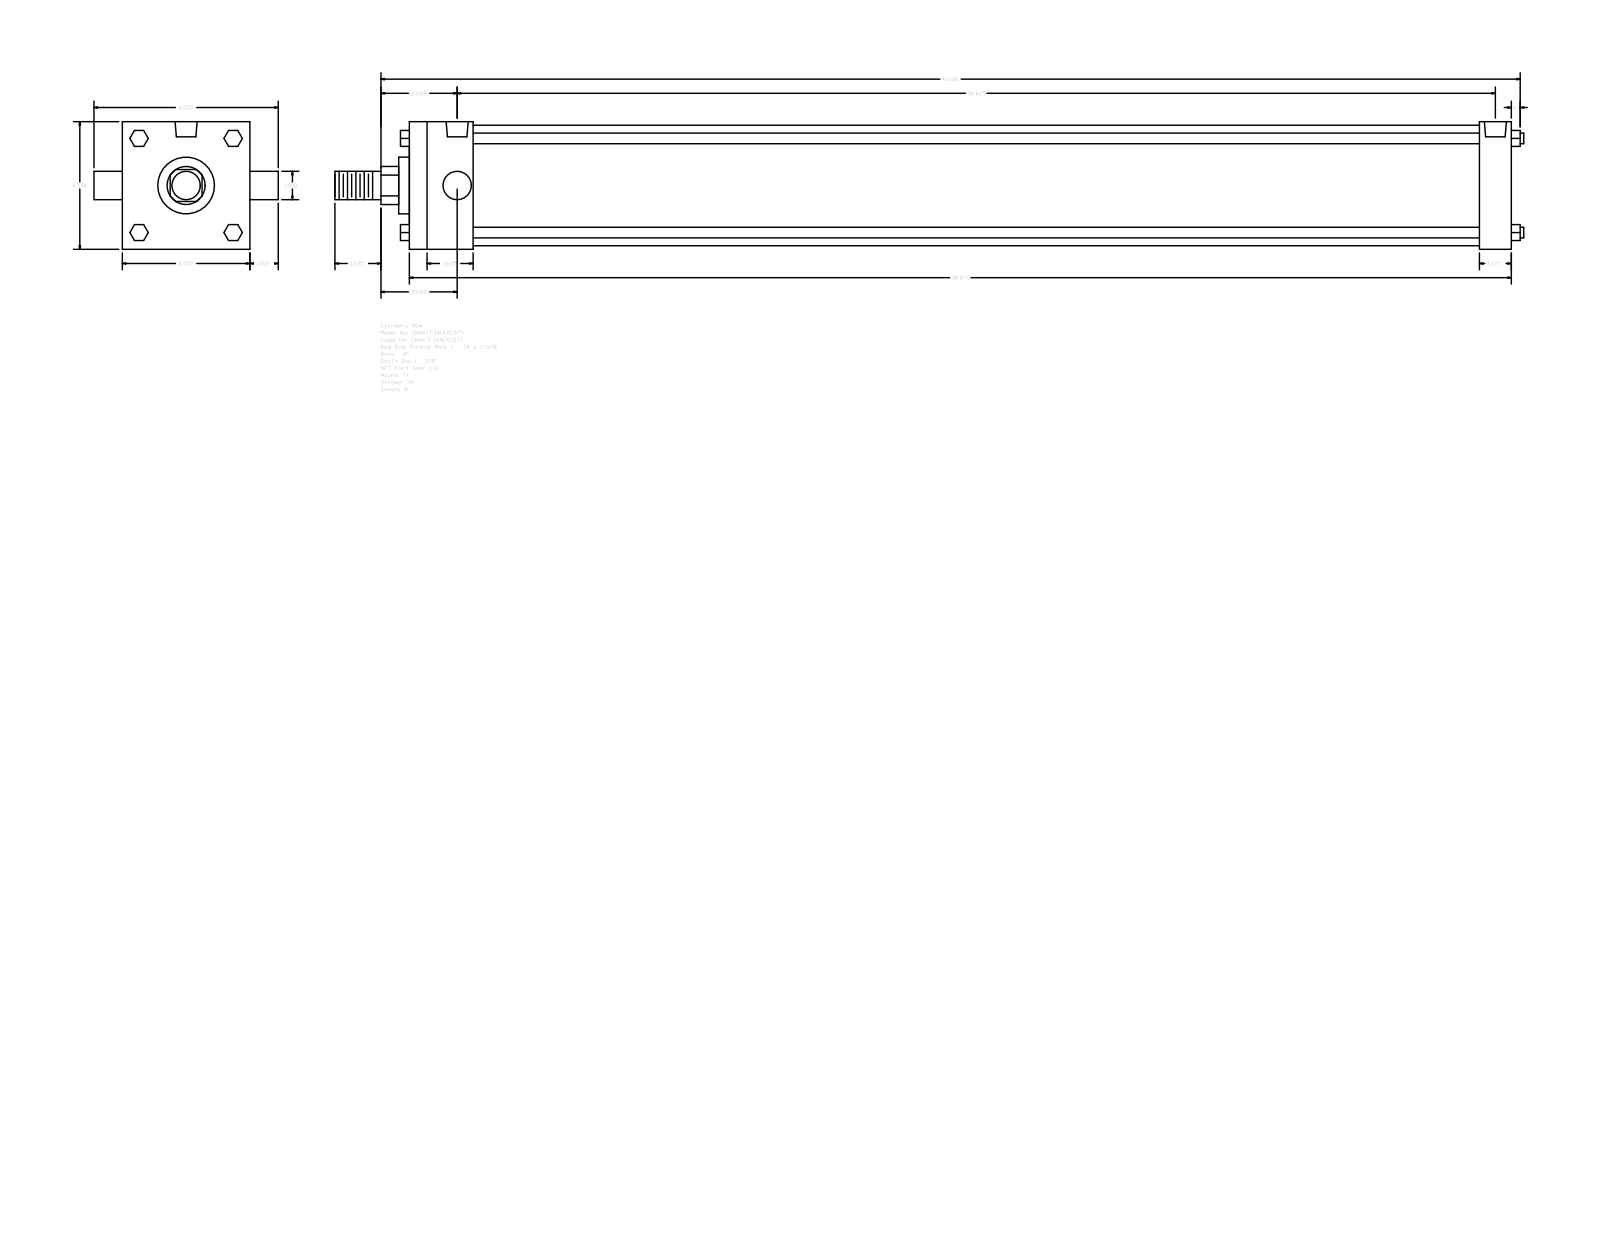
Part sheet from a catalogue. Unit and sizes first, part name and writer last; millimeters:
Units: millimetres
Overall size (bounding box): 1065.21 × 165.1 × 114.3
Round holes (diameter × count): ⌀8.73 ×3, ⌀19.77 ×2
Round bosses / shafts (diameter × count): ⌀9.53 ×4, ⌀25.4 ×2, ⌀107.95 ×1, ⌀50.8 ×1, ⌀34.92 ×1
Partial cylindrical surfaces — rounded edges, fillets, slot ends (radius × count): R17.06 ×1
Main face-to-face distances: 114.3, 987.43, 57.15, 28.58, 958.85, 901.7, 930.28, 66.67, 14.29, 25.4
Hole centre spacings: 3.18, 927.1, 923.92, 930.28
Bodies: 0 solids, 120 faces (92 planar, 28 cylindrical, 0 other)
Part name (STEP PRODUCT): A_TF__0400_1.375
STEP written by: GSSL Pune (CONFIG_CONTROL_DESIGN)
